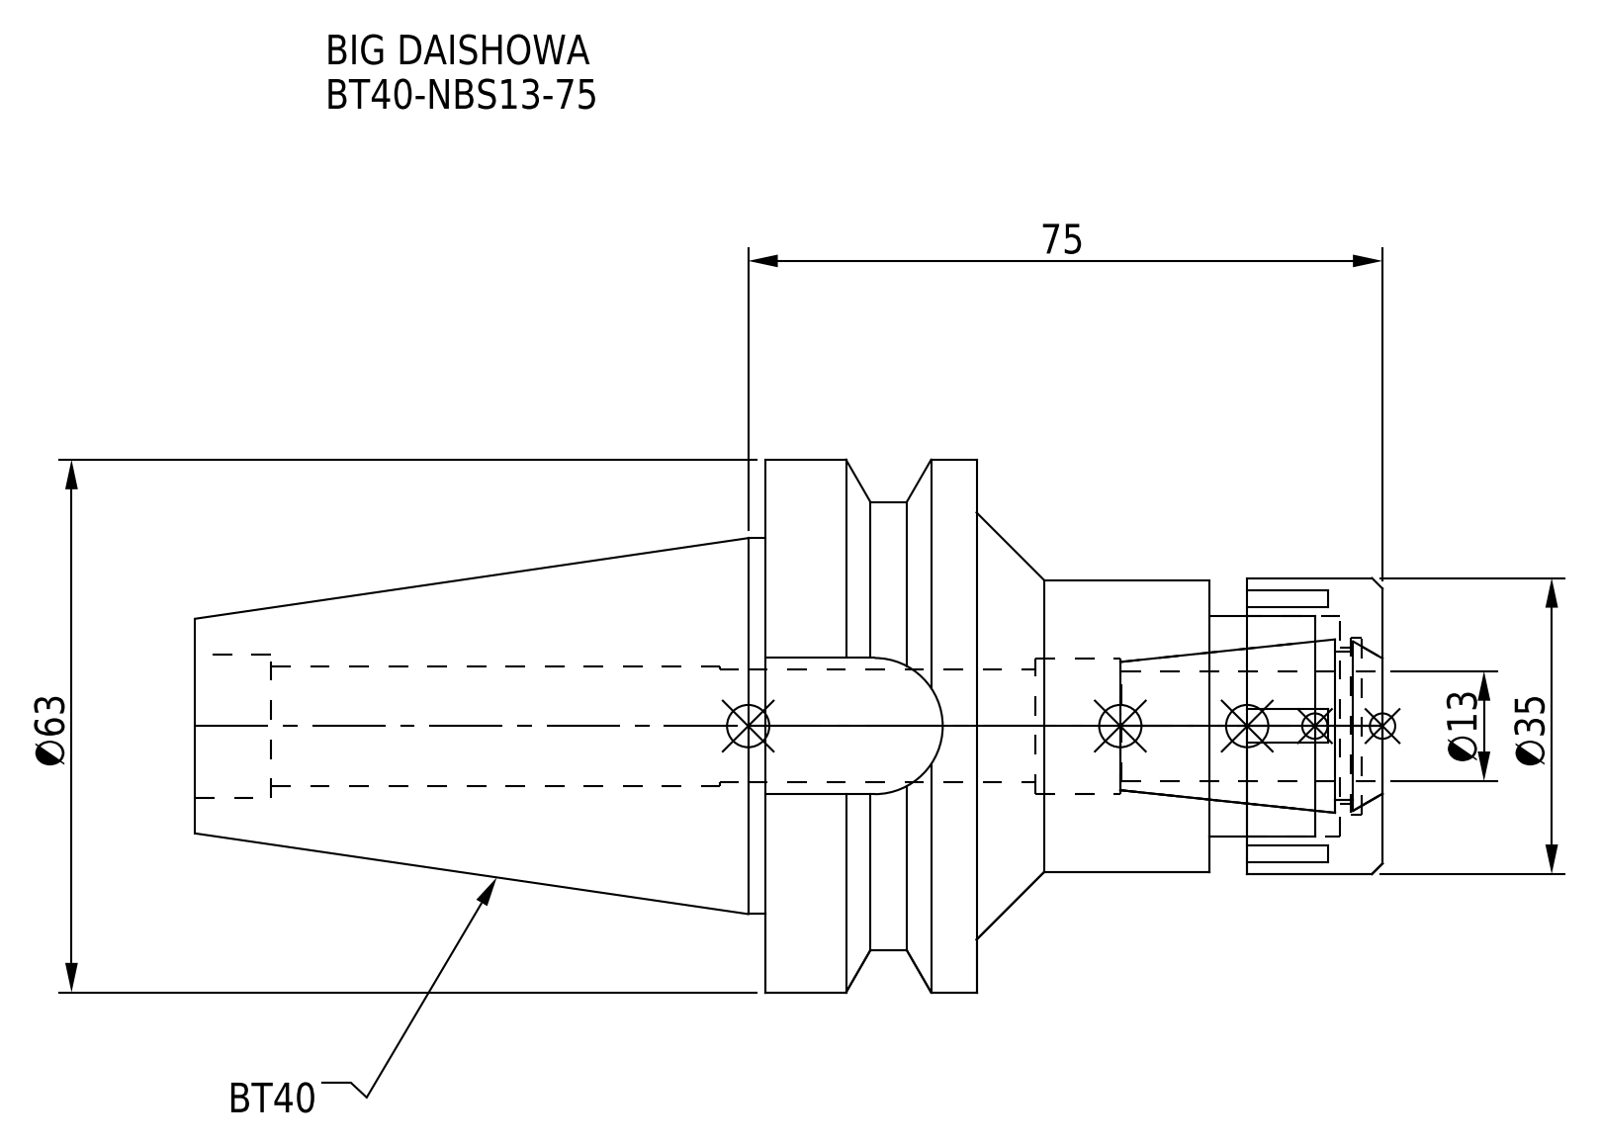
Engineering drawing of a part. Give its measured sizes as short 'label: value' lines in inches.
name: NBN13_1.stp; BT40-NBS13-75; BT40NB13075-130_ASM.stp; BT40-NBS13-75_1.stp (+3 more)
written by: SolidWorks 2019 (CONFIG_CONTROL_DESIGN)
unit: in
bodies: 2 solids, 90 faces (44 planar, 32 cylindrical, 14 other)
size: 5.528 × 2.48 × 2.48
volume: 9.454 in³; area: 50.95 in²
holes: 1× ⌀0.524, 1× ⌀0.559, 1× ⌀0.63, 1× ⌀0.669, 1× ⌀0.728, 1× ⌀0.827, 1× ⌀1.024
bosses: 1× ⌀2.48, 1× ⌀2.087, 1× ⌀1.75, 1× ⌀1.378, 1× ⌀1.358
rounds: 1× R0.317
face distances: 0.984, 1.89, 2.874, 0.807, 1.26, 0.315, 1.083, 2.067, 0.63, 0.177
